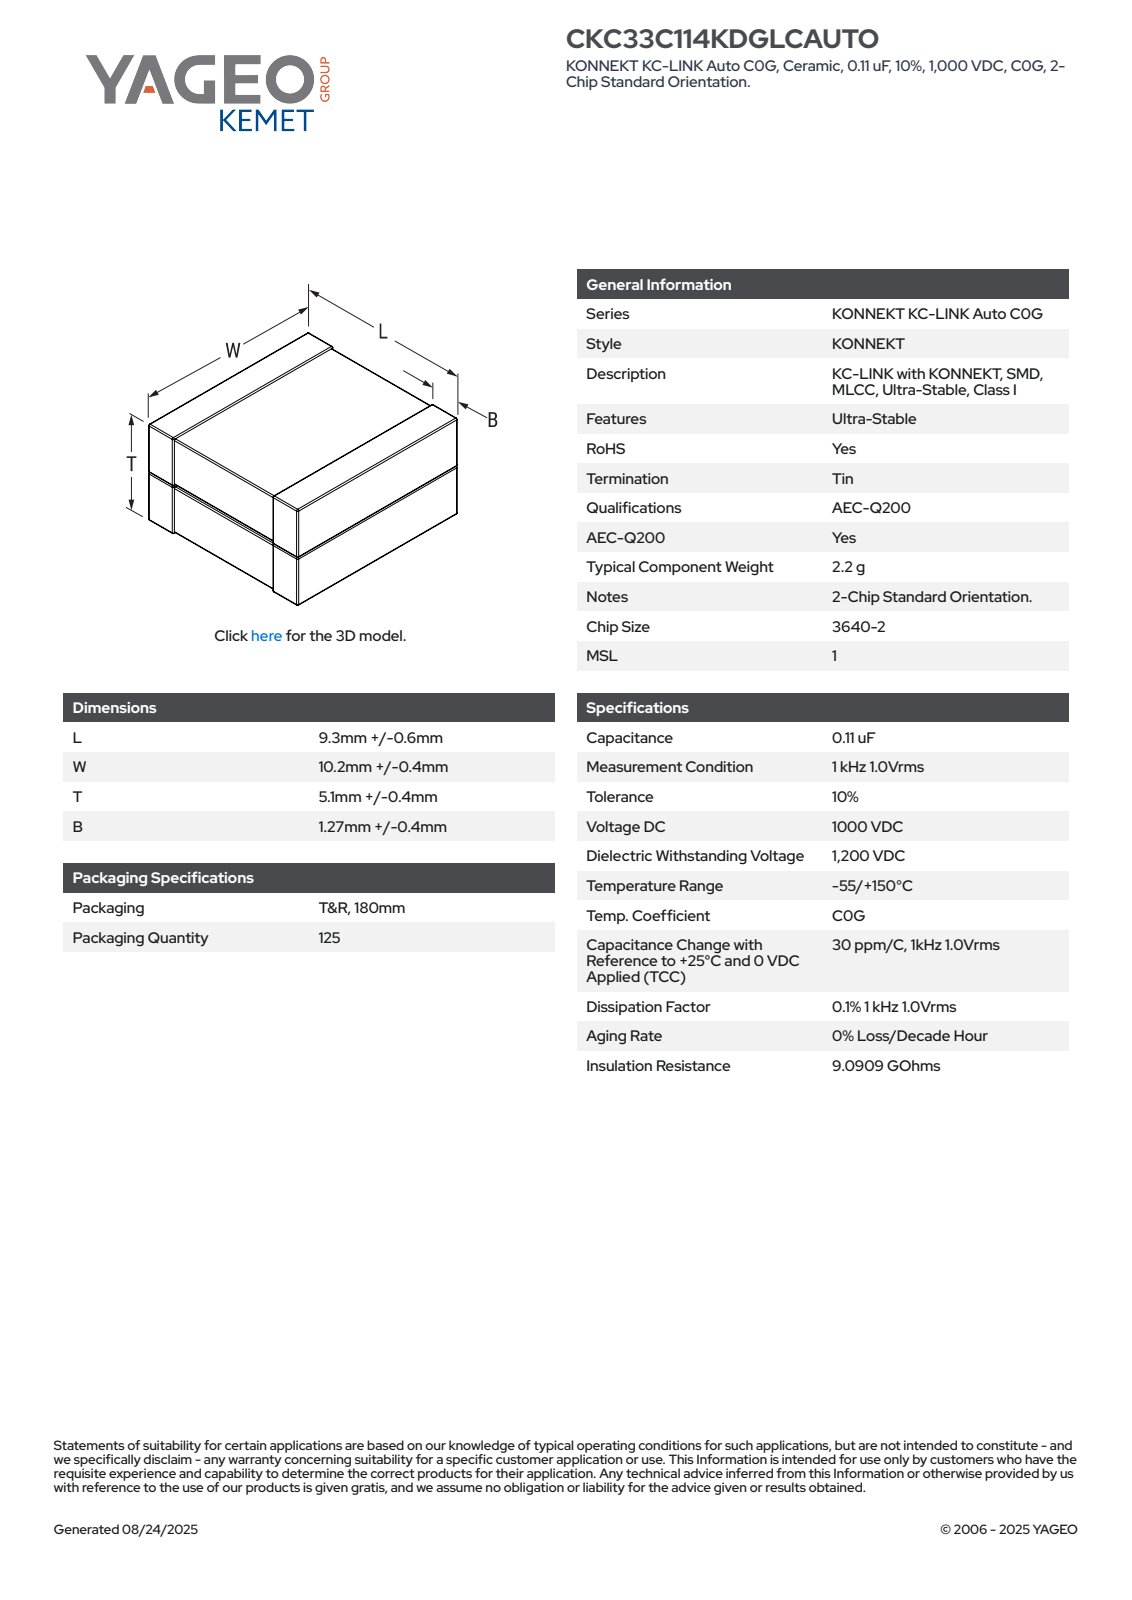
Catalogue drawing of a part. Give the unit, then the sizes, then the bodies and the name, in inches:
Units: inches
Overall size (bounding box): 0.417 × 0.39 × 0.217
Main face-to-face distances: 0.103, 0.108, 0.211, 0.106, 0.111, 0.214, 0.39, 0.412, 0.217, 0.415
Volume: 0.034 in³ · Surface area: 0.902 in²
Bodies: 4 solids, 189 faces (81 planar, 76 cylindrical, 32 other)
Part name (STEP PRODUCT): CCSS_K2T_3640_L9.9W10.6B1.67T5.5
STEP written by: SolidWorks 2020 (AUTOMOTIVE_DESIGN)
